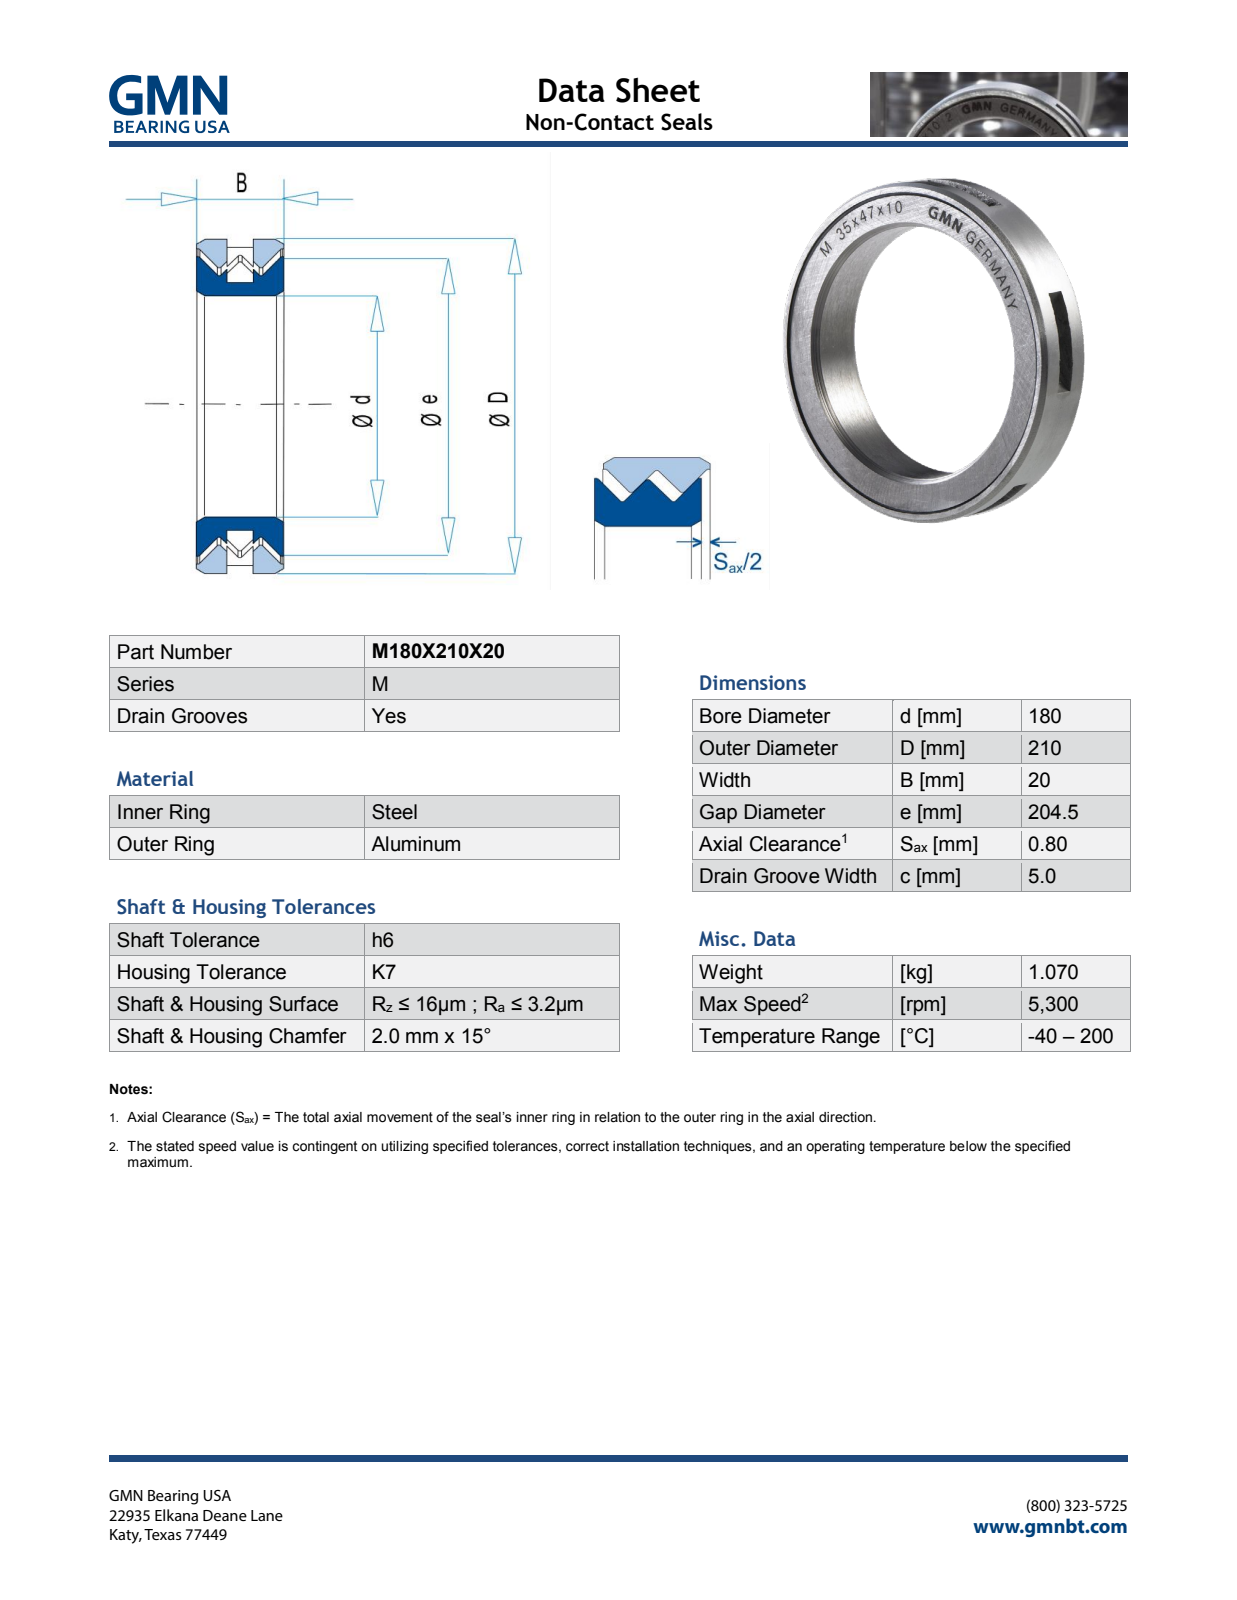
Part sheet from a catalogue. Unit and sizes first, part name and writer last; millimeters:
Units: millimetres
Overall size (bounding box): 210 × 210 × 20.08
Round holes (diameter × count): ⌀180 ×1, ⌀203.91 ×1
Round bosses / shafts (diameter × count): ⌀210 ×1
Partial cylindrical surfaces — rounded edges, fillets, slot ends (radius × count): R10 ×11
Main face-to-face distances: 20, 7.5, 12.5, 5, 7.58, 12.58, 20.08, 1.14, 7.96, 1.13
Volume: 170 111 mm³ · Surface area: 73 991 mm²
Bodies: 1 solid, 772 faces (641 planar, 41 cylindrical, 90 other)
Part name (STEP PRODUCT): M180X210X20_PRT
STEP written by: PRO/ENGINEER BY PARAMETRIC TECHNOLOGY CORPORATION, 2013150 (AUTOMOTIVE_DESIGN)
